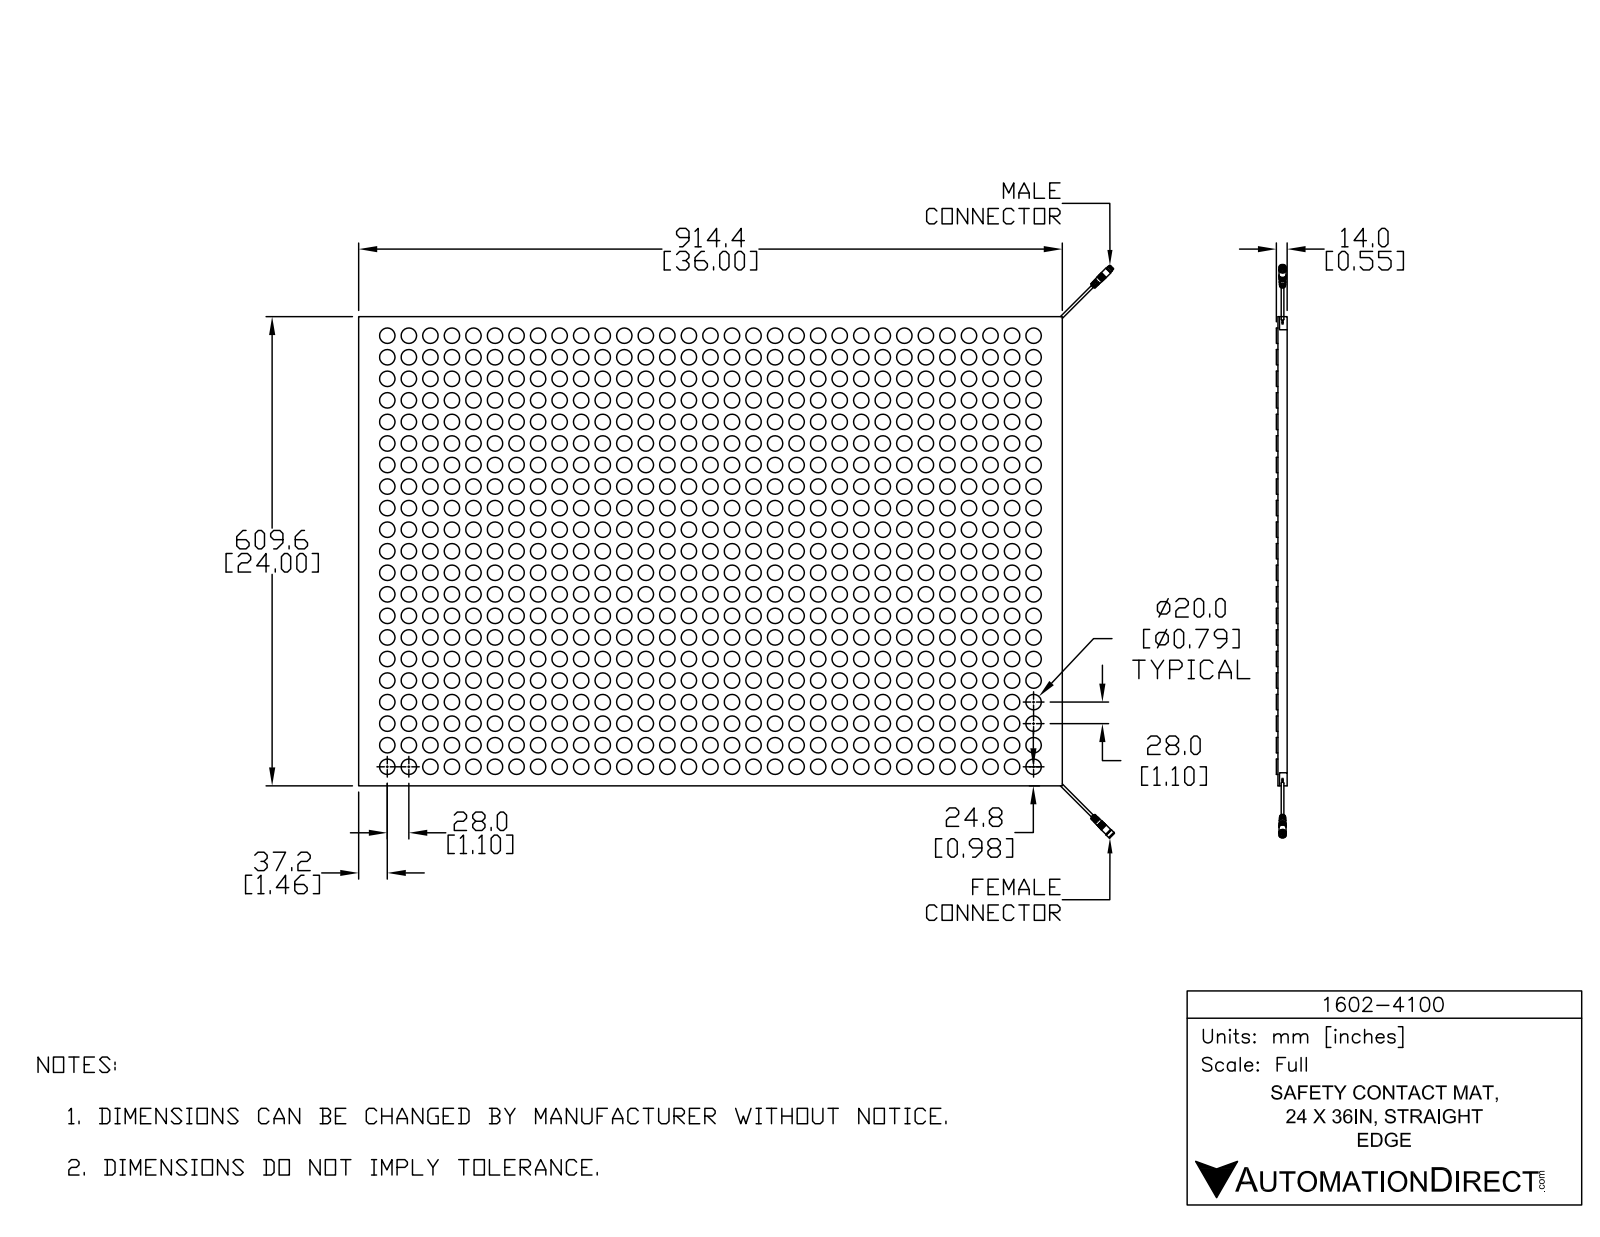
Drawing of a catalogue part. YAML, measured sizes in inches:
part_name: "1602-4100"
step_written_by: "SolidWorks 2018 (AUTOMOTIVE_DESIGN)"
units: inches
bodies: {solids: 20, faces: 1578, planar: 779, cylindrical: 710, other: 89}
overall_size: [38.67, 29.295, 0.551]
volume: 433.2
surface_area: 1920
round_holes:
  - {diameter: 0.063, count: 3}
  - {diameter: 0.134, count: 2}
  - {diameter: 0.228, count: 1}
  - {diameter: 0.232, count: 1}
  - {diameter: 0.272, count: 1}
  - {diameter: 0.283, count: 1}
round_bosses_or_shafts:
  - {diameter: 0.787, count: 651}
  - {diameter: 0.047, count: 24}
  - {diameter: 0.031, count: 8}
  - {diameter: 0.039, count: 3}
  - {diameter: 0.346, count: 2}
  - {diameter: 0.138, count: 2}
  - {diameter: 0.378, count: 1}
  - {diameter: 0.354, count: 1}
face_to_face_distances: [0.472, 0.079, 0.551, 24, 36, 0.157, 0.394, 0.087, 0.039, 3.8]
hole_center_spacings: [0.069, 0.097, 0.137]
